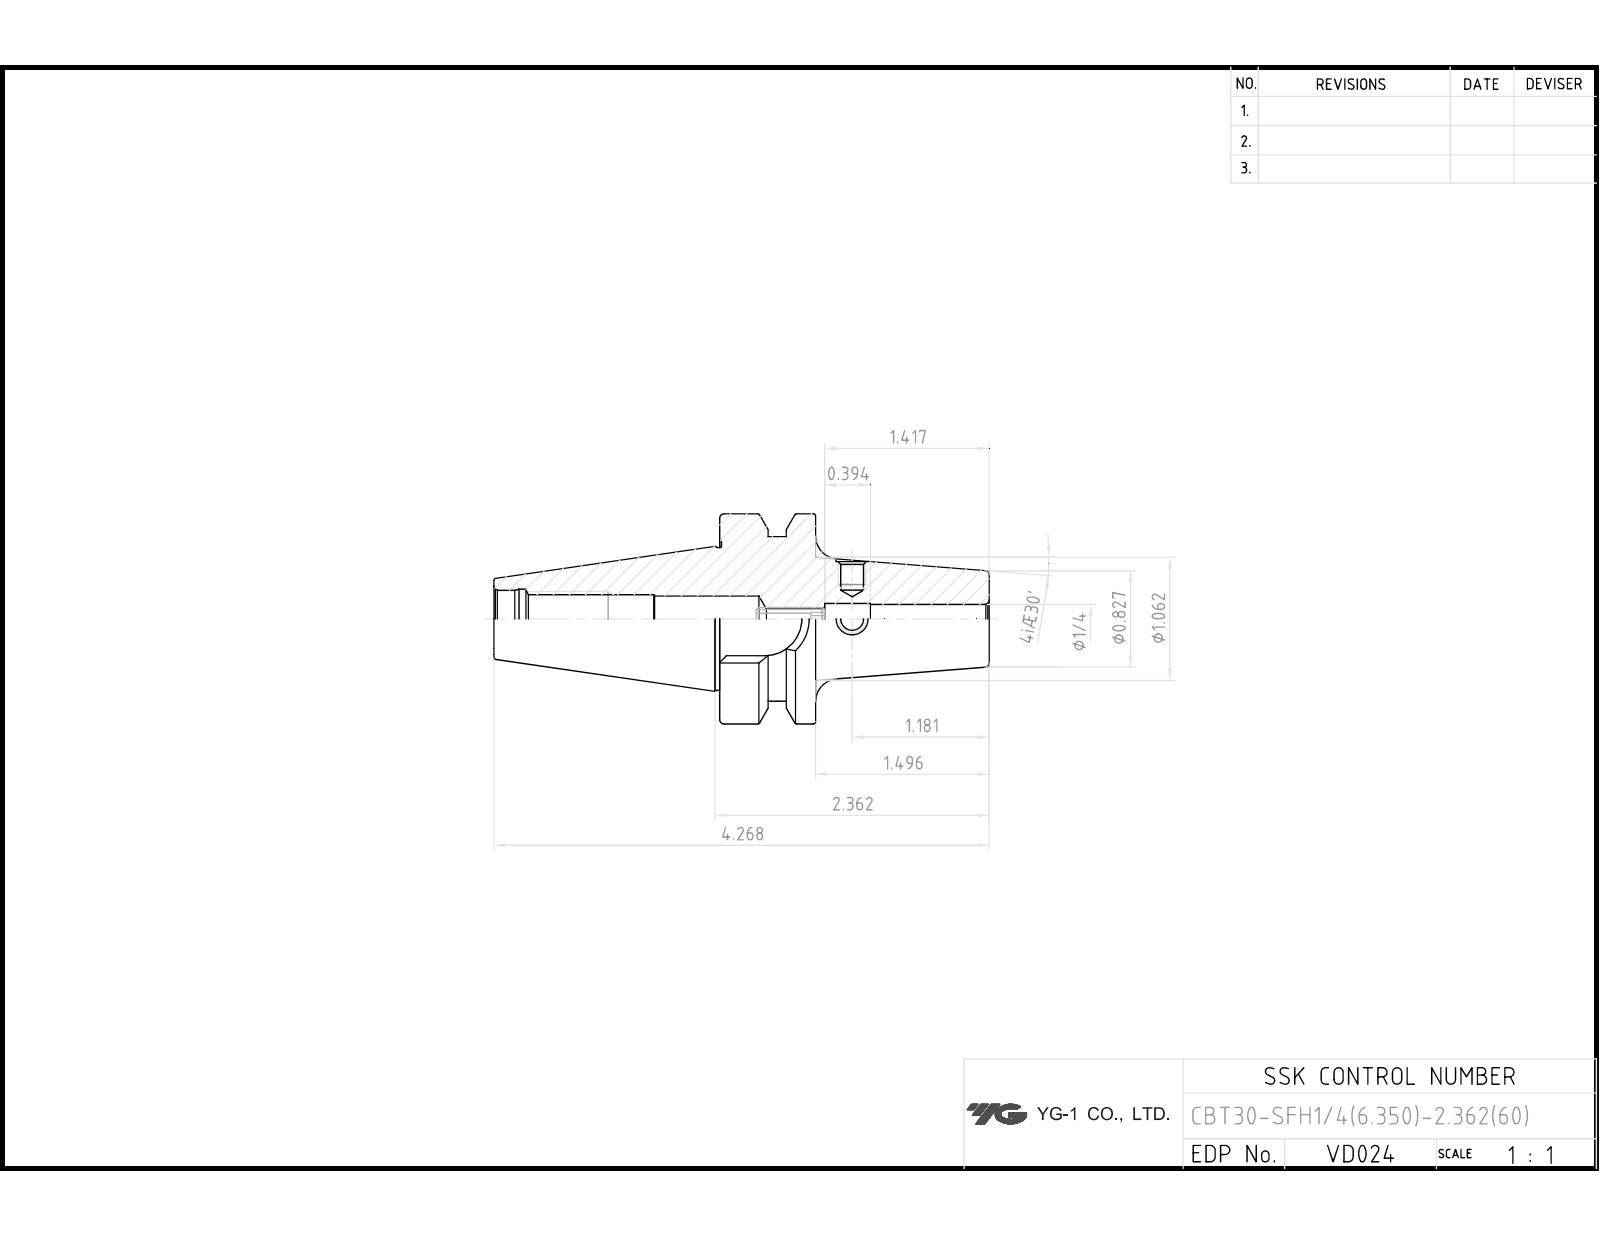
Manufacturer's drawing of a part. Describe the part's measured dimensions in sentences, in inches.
The part is named "CBT30-SFH6_35-60". Its 3-D file was written by "CREO PARAMETRIC BY PTC INC, 2018500 (CONFIG_CONTROL_DESIGN)". It is 1 solid with 104 faces: 28 planar, 32 cylindrical and 44 other. Overall it measures 4.268 by 1.811 by 1.811 inches. Its volume is 3.941 cubic inches and its surface area 25.58 square inches. Round holes: 1 of diameter 0.165, 1 of diameter 0.197, 1 of diameter 0.25, 1 of diameter 0.266, 1 of diameter 0.394, 1 of diameter 0.402, 1 of diameter 0.472, 1 of diameter 0.492, 1 of diameter 0.516. Round bosses or shafts: 1 of diameter 1.811, 1 of diameter 1.228. Partial cylindrical surfaces (rounded edges, fillets, slot ends): 1 of radius 0.317, 1 of radius 0.709. The main face-to-face distances are 0.827, 1.283, 2.323, 1.496, 0.576, 0.251, 1.747, 0.419, 0.157, 0.408.
